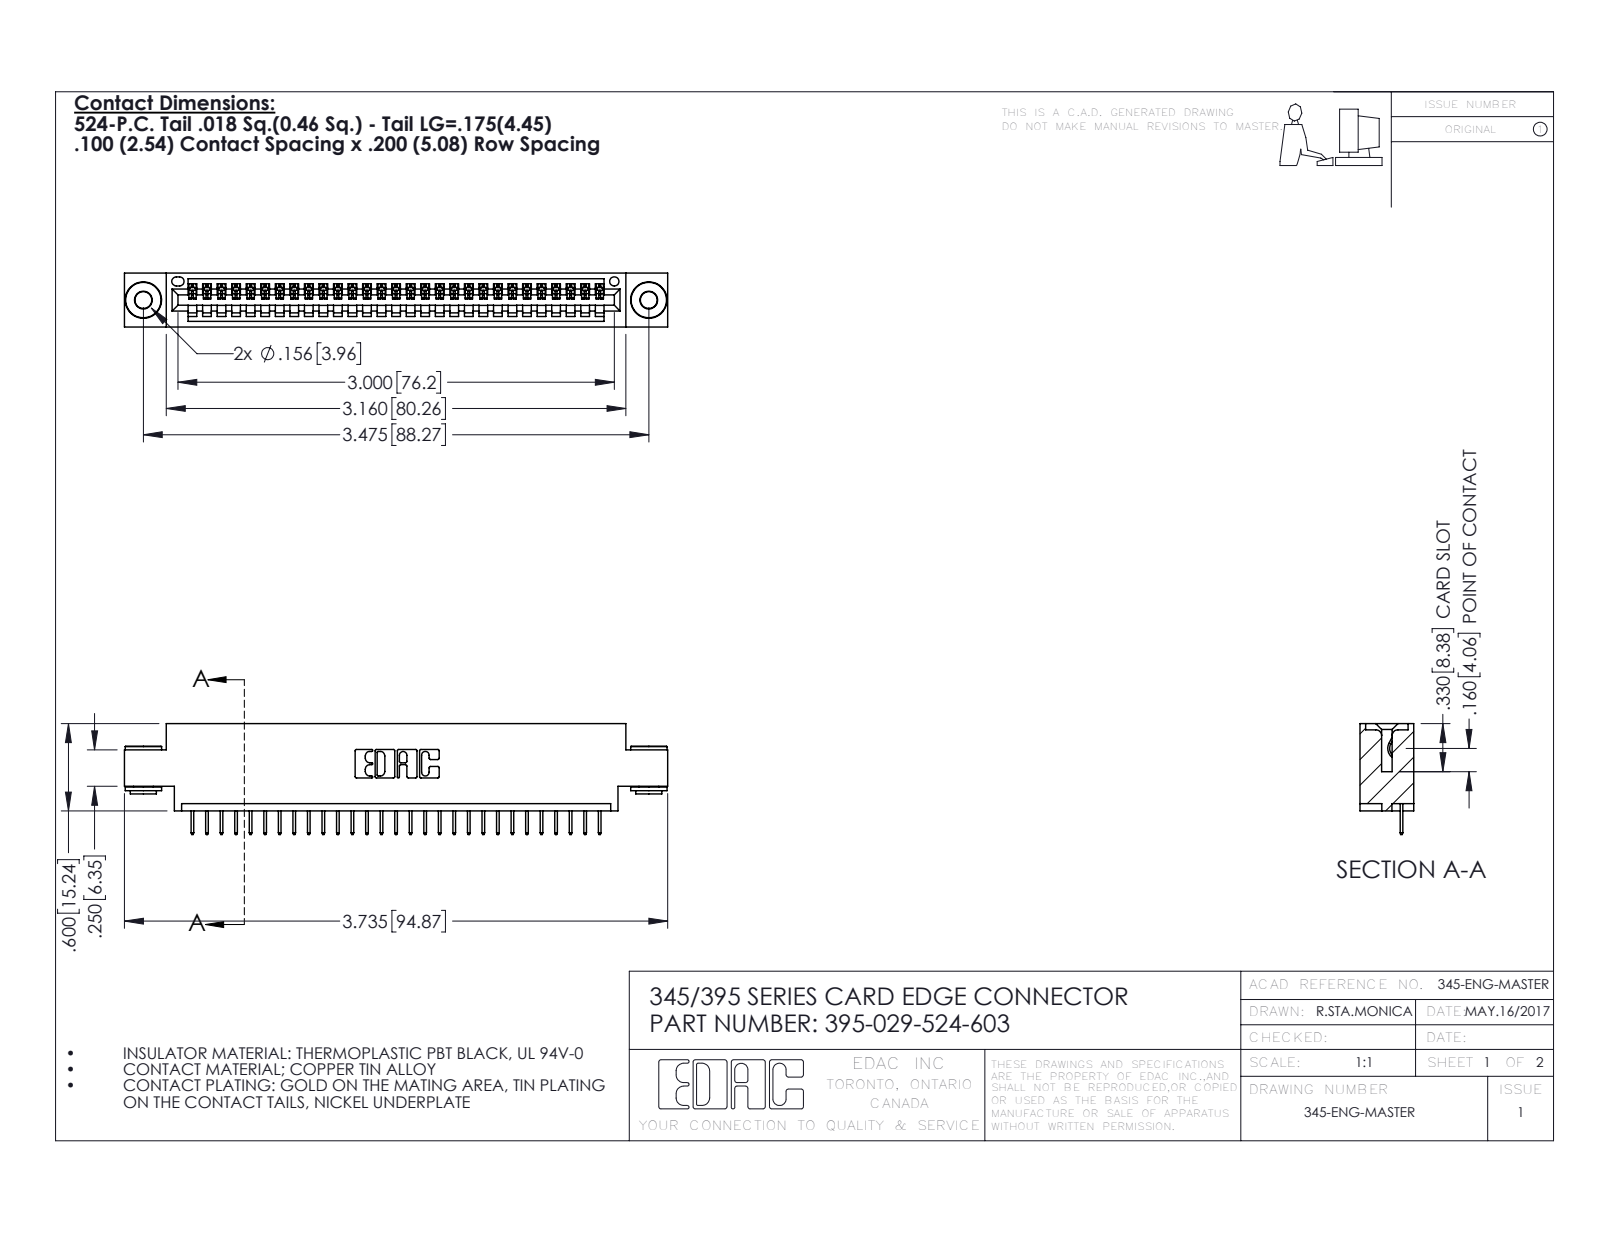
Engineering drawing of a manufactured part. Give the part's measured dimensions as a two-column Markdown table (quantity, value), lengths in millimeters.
| quantity | value |
| --- | --- |
| part name | 395-029-524-603; 345-250-002_345-250-002-102; 345-292-001_345-293-124; 345 Part_0.170 Offset - 0.156 Dia-TH |
| STEP written by | SolidWorks 2016 (CONFIG_CONTROL_DESIGN) |
| units | millimeters |
| bodies | 32 solids, 1966 faces (1428 planar, 530 cylindrical, 8 other) |
| overall size | 94.9 × 19.4 × 9.4 |
| volume | 8 700 mm³ |
| surface area | 11 350 mm² |
| round holes (diameter × count) | 2.9 × 2, 4 × 2, 1.6 × 1 |
| round bosses / shafts (diameter × count) | 6.4 × 2, 4.6 × 2, 3.5 × 2 |
| partial cylindrical surfaces (radius × count) | 0.2 × 58, 0.3 × 22, 0.2 × 6, 0.8 × 6, 0.7 × 3, 0.8 × 2, 1 × 2, 0.4 × 1 |
| main face-to-face distances | 1.8, 7.6, 9.4, 5.1, 2.5, 6.9, 0.6, 5.7, 4.4, 1.8 |
| hole center spacings | 6.9, 82.3, 88.3 |
